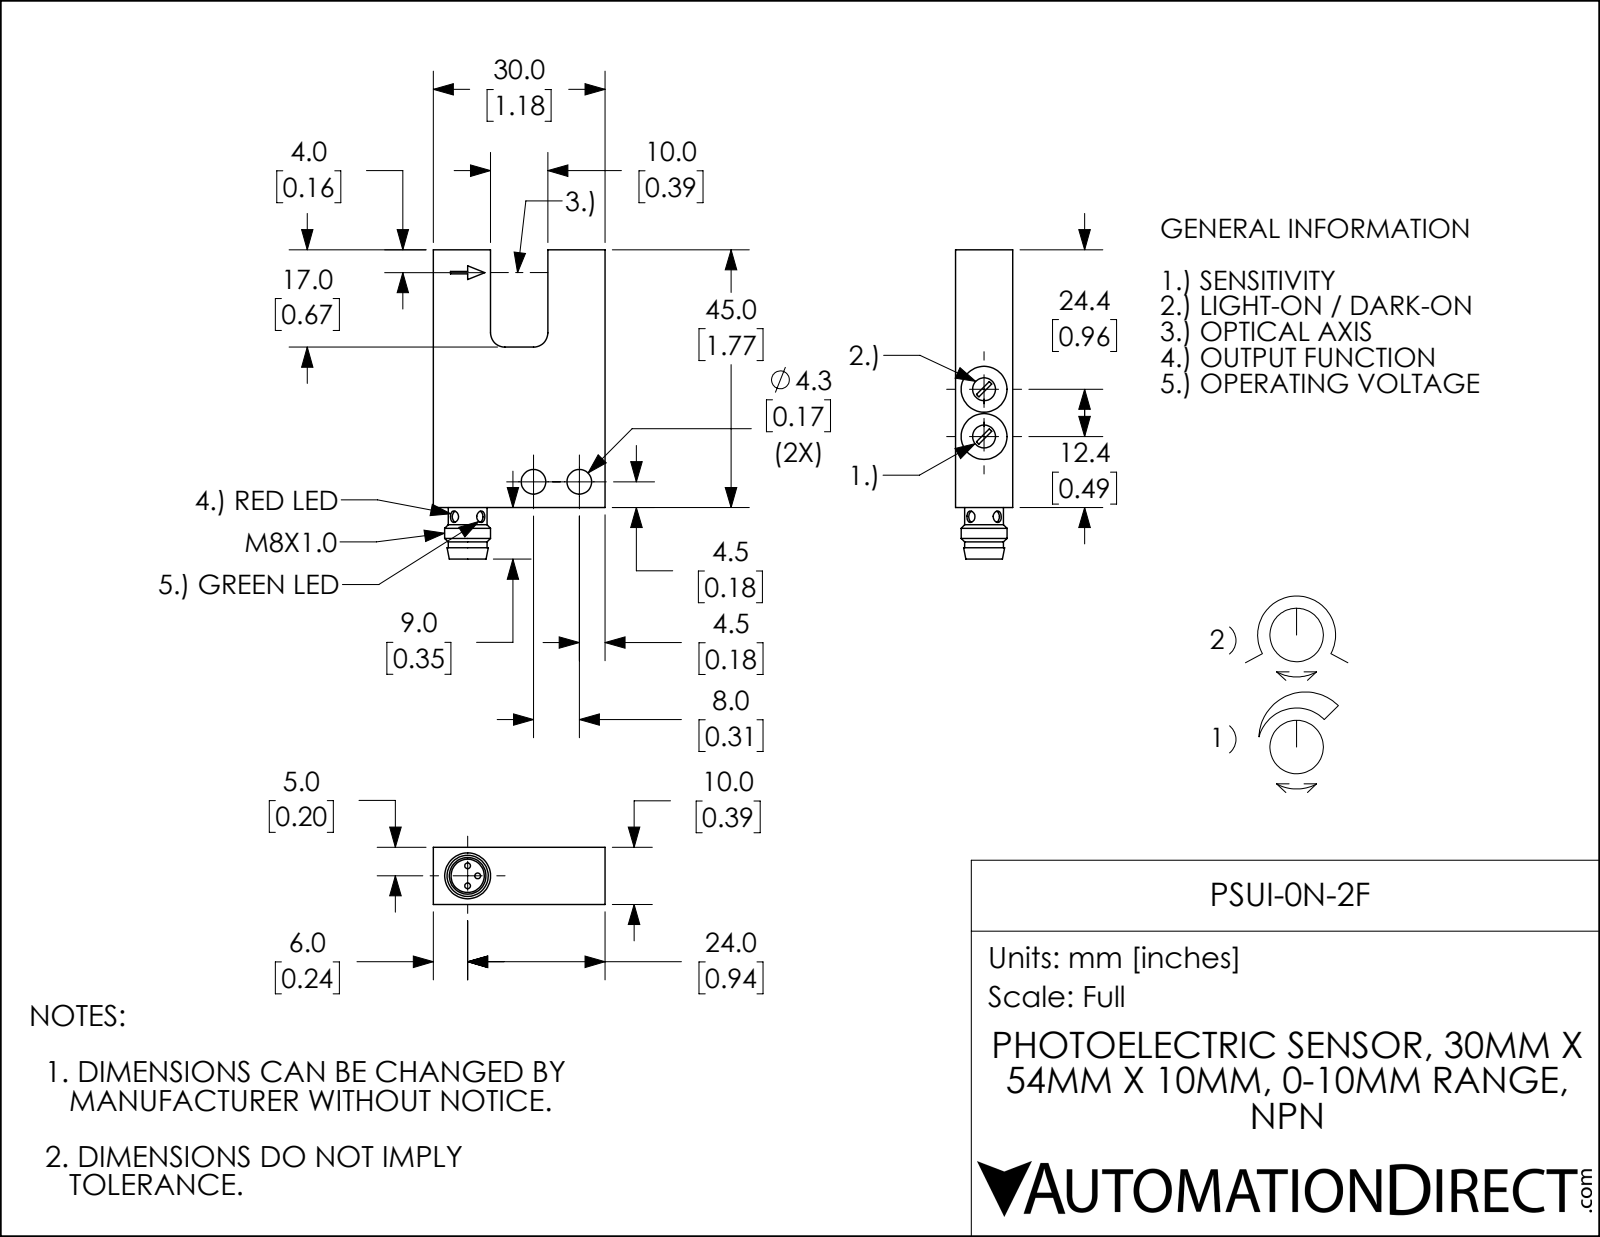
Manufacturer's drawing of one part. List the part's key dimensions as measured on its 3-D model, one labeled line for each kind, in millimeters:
Part name (STEP PRODUCT): PSUI-0N-2F
STEP written by: SolidWorks 2017 (AUTOMOTIVE_DESIGN)
Units: millimetres
Bodies: 1 solid, 64 faces (35 planar, 23 cylindrical, 6 other)
Overall size (bounding box): 54 × 30 × 10
Volume: 11 700 mm³ · Surface area: 4 770 mm²
Round holes (diameter × count): ⌀2 ×2, ⌀4 ×2, ⌀4.3 ×2, ⌀8 ×2, ⌀5.8 ×1
Round bosses / shafts (diameter × count): ⌀1 ×3, ⌀8 ×1, ⌀6.8 ×1
Partial cylindrical surfaces — rounded edges, fillets, slot ends (radius × count): R1.6 ×2, R2.5 ×2
Main face-to-face distances: 10, 30, 20, 45, 9.9, 29.9, 19.9, 17, 28, 4
Hole centre spacings: 8, 8.3
